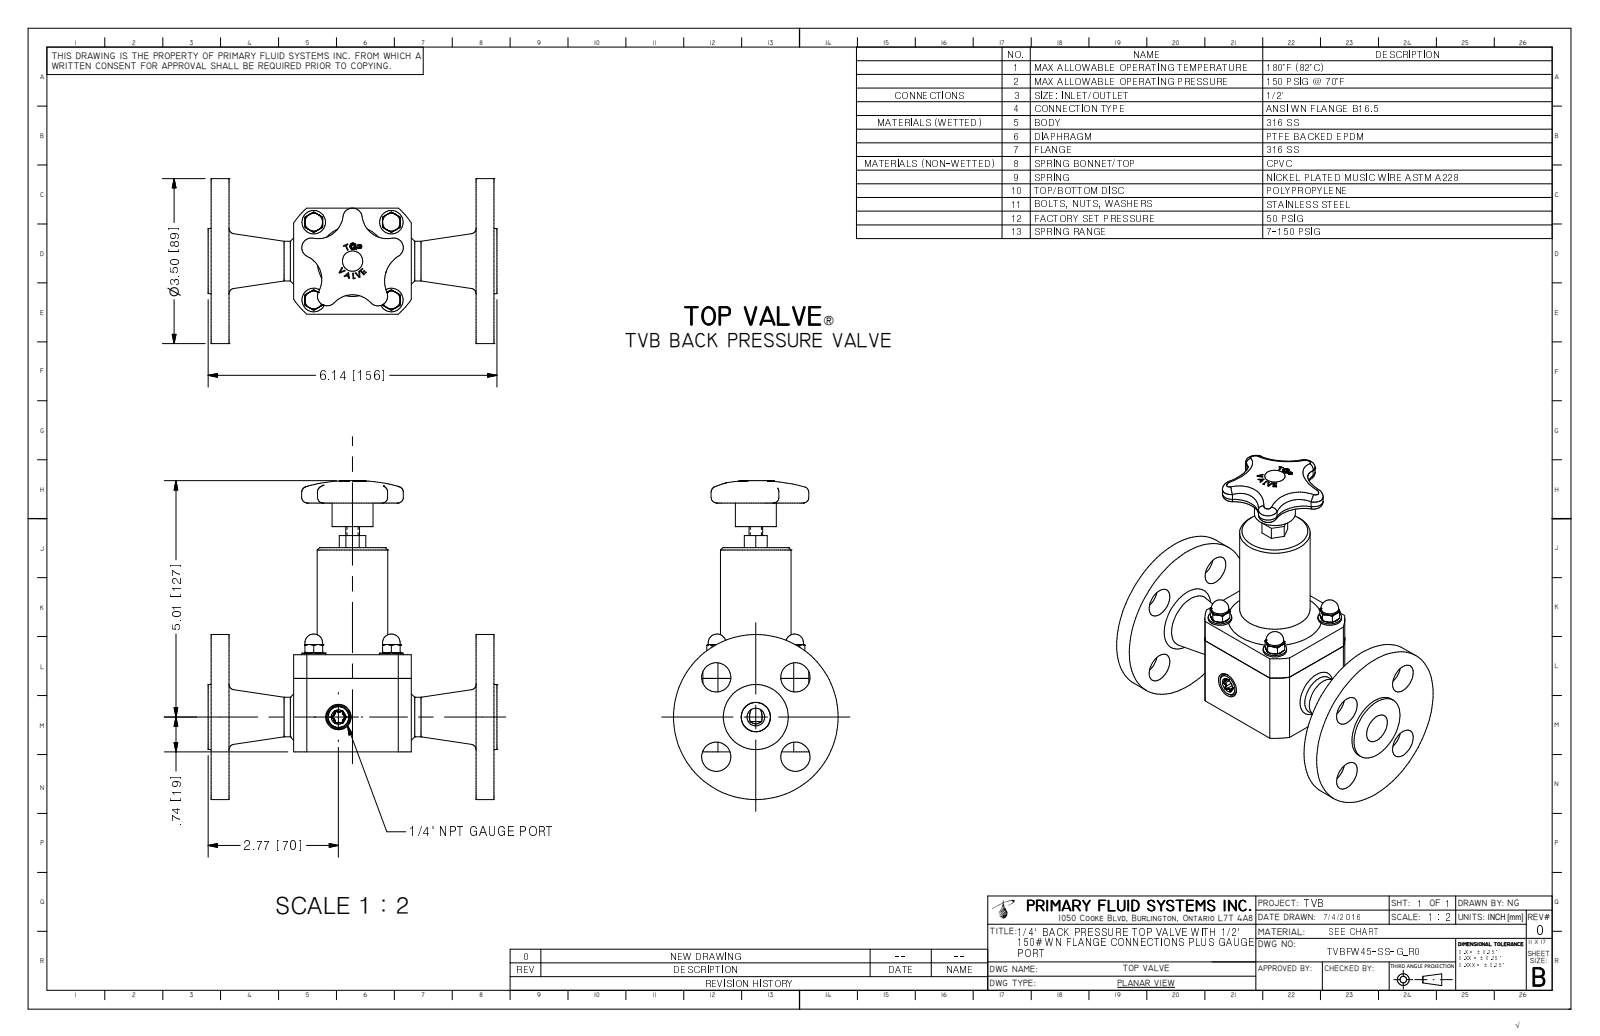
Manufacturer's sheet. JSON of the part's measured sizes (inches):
{"part_name": "TVBFW45-SS-G-R0", "step_written_by": "Autodesk Inventor 2009 (AUTOMOTIVE_DESIGN)", "units": "inches", "bodies": {"solids": 6, "faces": 433, "planar": 169, "cylindrical": 77, "other": 187}, "overall_size": [6.762, 6.14, 3.5], "volume_in3": 22.41, "surface_area_in2": 131.2, "round_holes": [[0.62, 5], [0.156, 1], [0.313, 1], [0.375, 1], [0.438, 1], [0.622, 1], [0.76, 1], [0.9, 1], [1.115, 1], [1.525, 1]], "round_bosses_or_shafts": [[0.5, 4], [0.375, 4], [0.312, 4], [0.147, 4], [3.5, 1], [1.5, 1], [1.38, 1], [0.87, 1]], "partial_cylinders_radius": [[0.027, 6], [0.085, 5], [0.205, 5], [0.536, 4], [0.656, 4], [0.625, 1], [0.745, 1], [1.488, 1]], "face_to_face_distances": [0.38, 5.635, 6.015, 5.255, 1.757, 4.257, 1.378, 3.878, 2.25, 2.5], "hole_center_spacings": [1.19, 1.19, 1.683, 1.683, 2.38, 0.08]}
